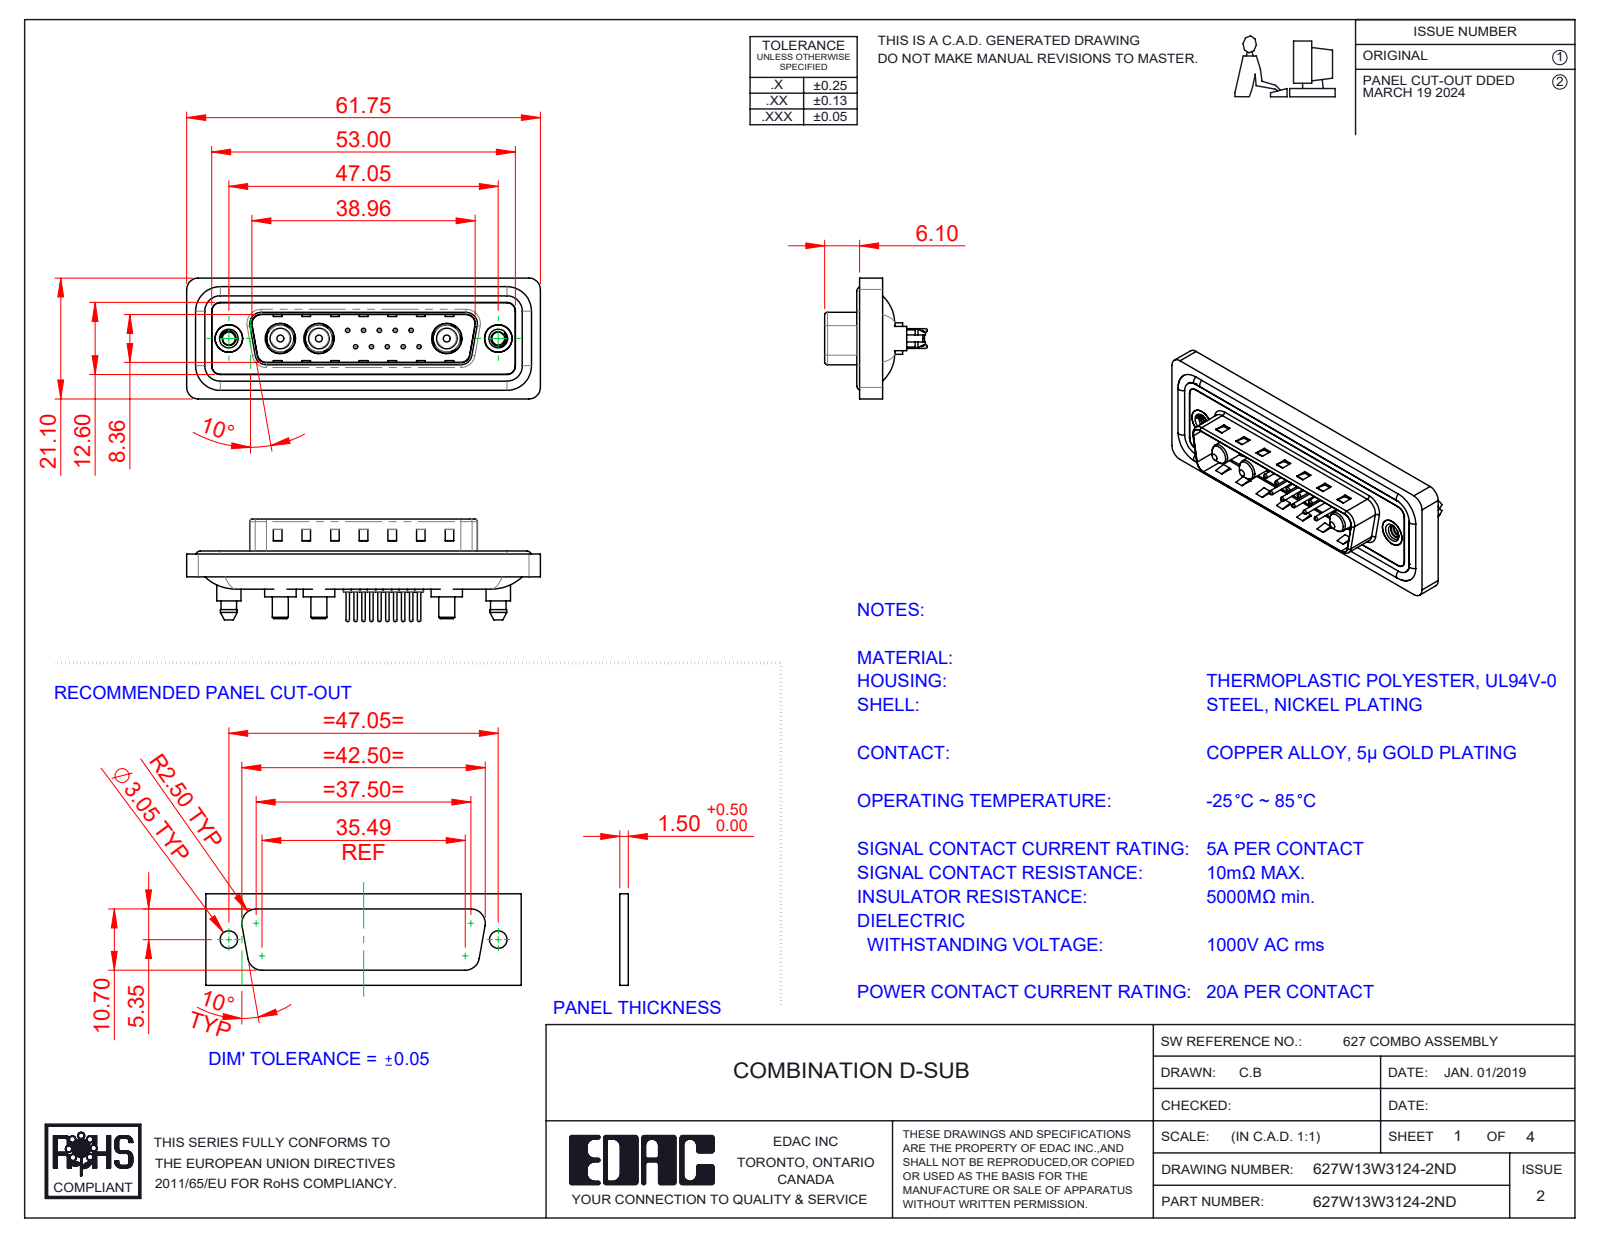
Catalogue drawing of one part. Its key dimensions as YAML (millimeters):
part_name: "627Combo Shell Front_25 Contacts; 627Combo Contact Row 1_24; 627Combo Shell Rear_25 Contacts; Power Pin_20A S (+6 more)"
step_written_by: "SolidWorks 2023 (CONFIG_CONTROL_DESIGN)"
units: millimeters
bodies: {solids: 23, faces: 1028, planar: 325, cylindrical: 425, other: 278}
overall_size: [61.75, 21.1, 17.9]
volume: 7470
surface_area: 12211
round_holes:
  - {diameter: 0.75, count: 10}
  - {diameter: 1.6, count: 10}
  - {diameter: 2, count: 10}
  - {diameter: 4.85, count: 3}
  - {diameter: 5.3, count: 3}
  - {diameter: 2.26, count: 2}
  - {diameter: 4, count: 2}
  - {diameter: 4.8, count: 2}
  - {diameter: 5, count: 2}
round_bosses_or_shafts:
  - {diameter: 1.5, count: 10}
  - {diameter: 0.6, count: 10}
  - {diameter: 1.6, count: 4}
  - {diameter: 5.5, count: 3}
  - {diameter: 5.2, count: 3}
  - {diameter: 4.75, count: 3}
  - {diameter: 3.75, count: 3}
  - {diameter: 3.6, count: 3}
partial_cylinders:
  - {radius: 1.5, count: 24}
  - {radius: 2, count: 18}
  - {radius: 1.6, count: 10}
  - {radius: 0.5, count: 8}
  - {radius: 0.25, count: 4}
  - {radius: 0.6, count: 4}
  - {radius: 0.65, count: 4}
  - {radius: 0.9, count: 4}
face_to_face_distances: [0.4, 1.5, 1.1, 1.6, 0.5, 3.1, 2.9, 0.82, 9.58, 4.1]
hole_center_spacings: [3.16, 2.77, 5.04, 5.54, 7.49, 5.03, 8.31, 10.11]
